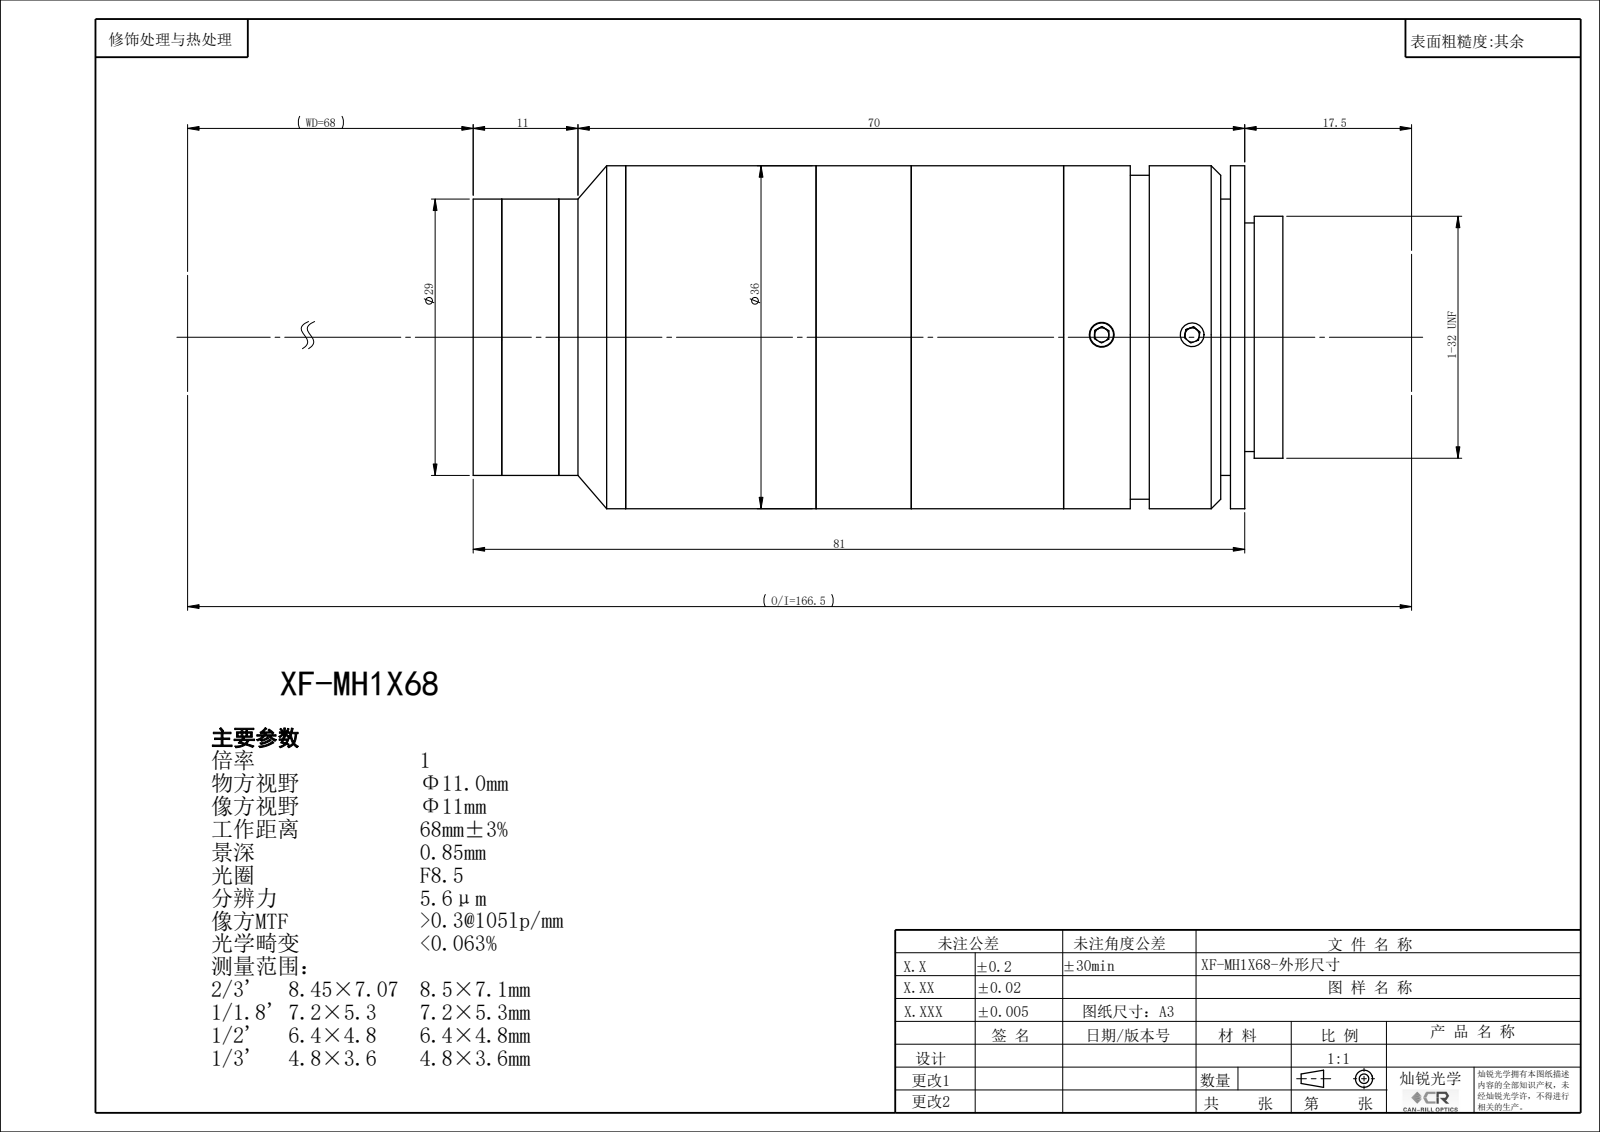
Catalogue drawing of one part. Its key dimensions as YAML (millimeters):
part_name: "XF-MH1X68"
step_written_by: "SolidWorks 2022 (CONFIG_CONTROL_DESIGN)"
units: millimeters
bodies: {solids: 0, faces: 130, planar: 64, cylindrical: 44, other: 22}
overall_size: [85.04, 36.02, 36]
round_holes:
  - {diameter: 2.5, count: 3}
  - {diameter: 14, count: 1}
  - {diameter: 22.4, count: 1}
  - {diameter: 24, count: 1}
  - {diameter: 24.9, count: 1}
  - {diameter: 26.4, count: 1}
  - {diameter: 27, count: 1}
round_bosses_or_shafts:
  - {diameter: 36, count: 1}
  - {diameter: 34, count: 1}
  - {diameter: 29, count: 1}
  - {diameter: 25.4, count: 1}
face_to_face_distances: [19.02, 58.22, 77.24, 1.5, 75.74, 17.52, 65.02, 42.22, 16, 33.52]
